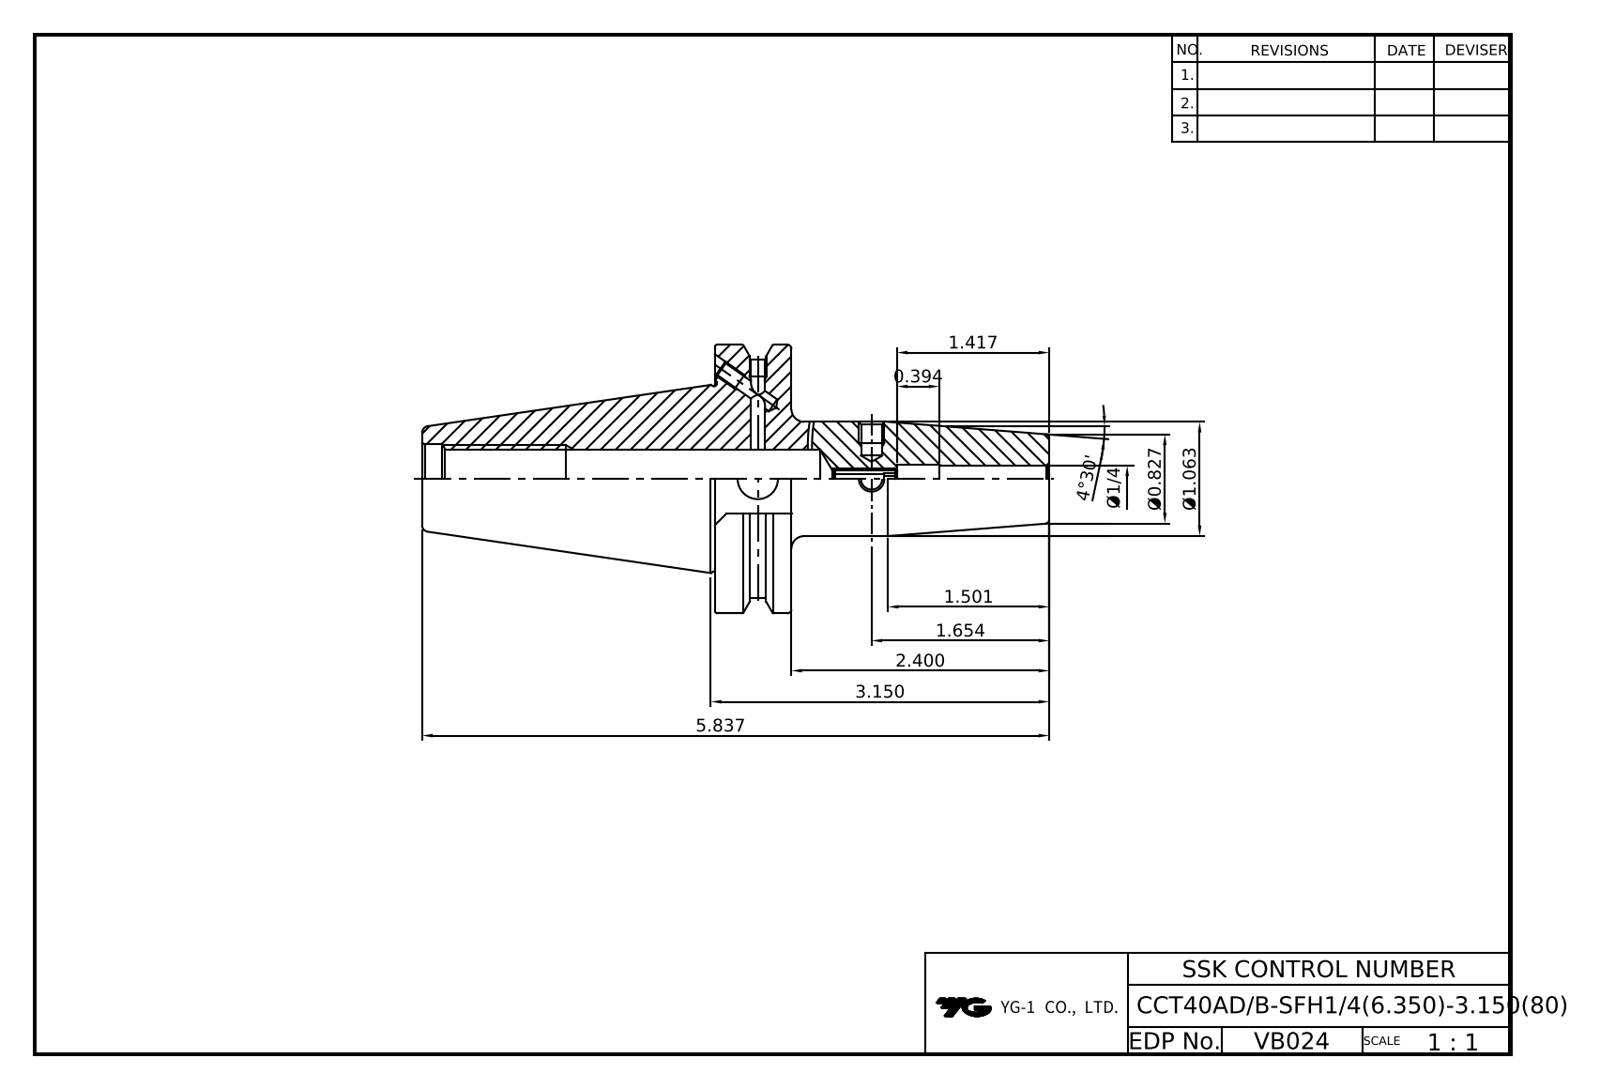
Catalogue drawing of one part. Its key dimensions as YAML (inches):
part_name: "LO CCT40ADB-SFH6.35-80"
step_written_by: "Autodesk Inventor 2022 (AUTOMOTIVE_DESIGN)"
units: inches
bodies: {solids: 1, faces: 89, planar: 38, cylindrical: 29, other: 22}
overall_size: [5.837, 2.5, 2.405]
volume: 8.042
surface_area: 41.75
round_holes:
  - {diameter: 0.128, count: 4}
  - {diameter: 0.157, count: 2}
  - {diameter: 0.165, count: 2}
  - {diameter: 0.169, count: 1}
  - {diameter: 0.25, count: 1}
  - {diameter: 0.297, count: 1}
  - {diameter: 0.375, count: 1}
  - {diameter: 0.512, count: 1}
  - {diameter: 0.527, count: 1}
  - {diameter: 0.642, count: 1}
round_bosses_or_shafts:
  - {diameter: 2.5, count: 1}
  - {diameter: 1.724, count: 1}
  - {diameter: 1.063, count: 1}
partial_cylinders:
  - {radius: 1.108, count: 1}
face_to_face_distances: [0.711, 3.11, 2.4, 1.874, 0.645, 2.726, 3.437, 5.837, 3.202, 0.476]
